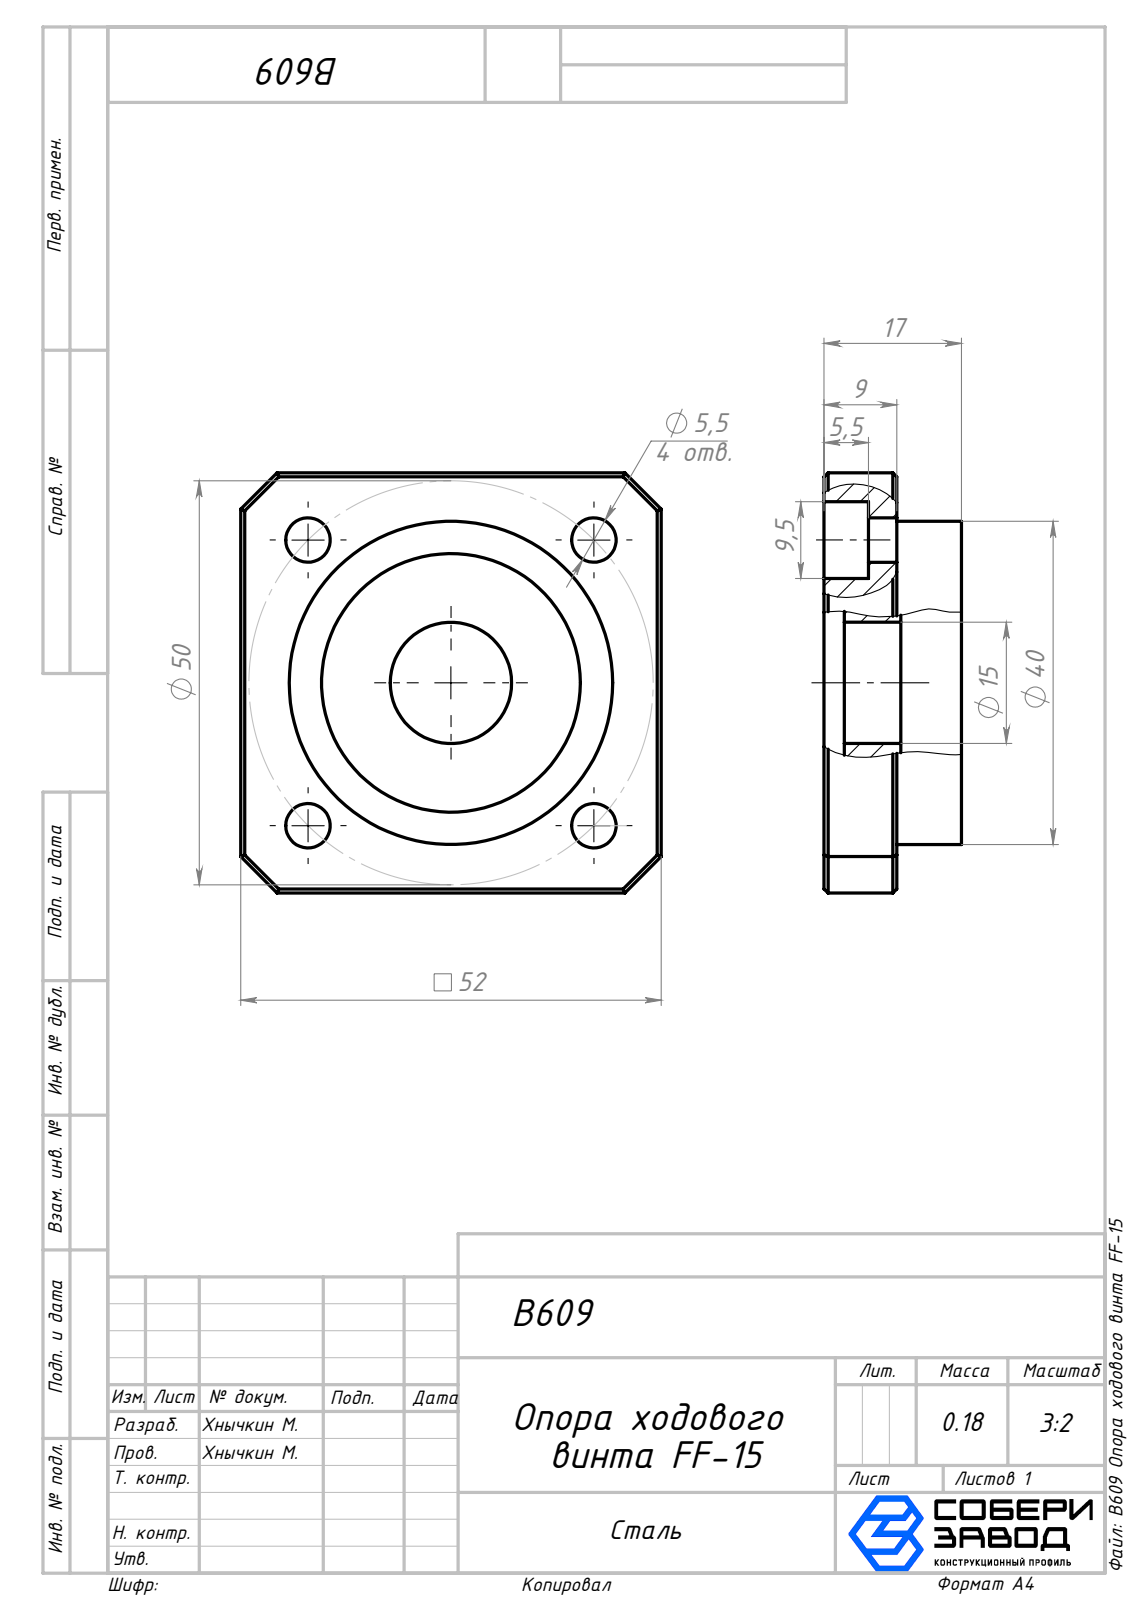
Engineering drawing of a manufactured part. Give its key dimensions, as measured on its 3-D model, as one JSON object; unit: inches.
{"part_name": "B609 Опора ходового винта FF-15", "step_written_by": "SolidWorks 2026 (AUTOMOTIVE_DESIGN)", "units": "inches", "bodies": {"solids": 2, "faces": 57, "planar": 33, "cylindrical": 24, "other": 0}, "overall_size": [2.047, 2.047, 0.669], "volume_in3": 1.392, "surface_area_in2": 17.19, "round_holes": [[0.217, 4], [0.374, 4], [0.591, 1], [1.26, 1]], "round_bosses_or_shafts": [[1.575, 1]], "face_to_face_distances": [0.354, 2.047, 0.098, 0.374, 0.256, 0.276, 0.02, 0.669, 0.571, 0.315], "hole_center_spacings": [0.984, 1.392, 1.969]}
